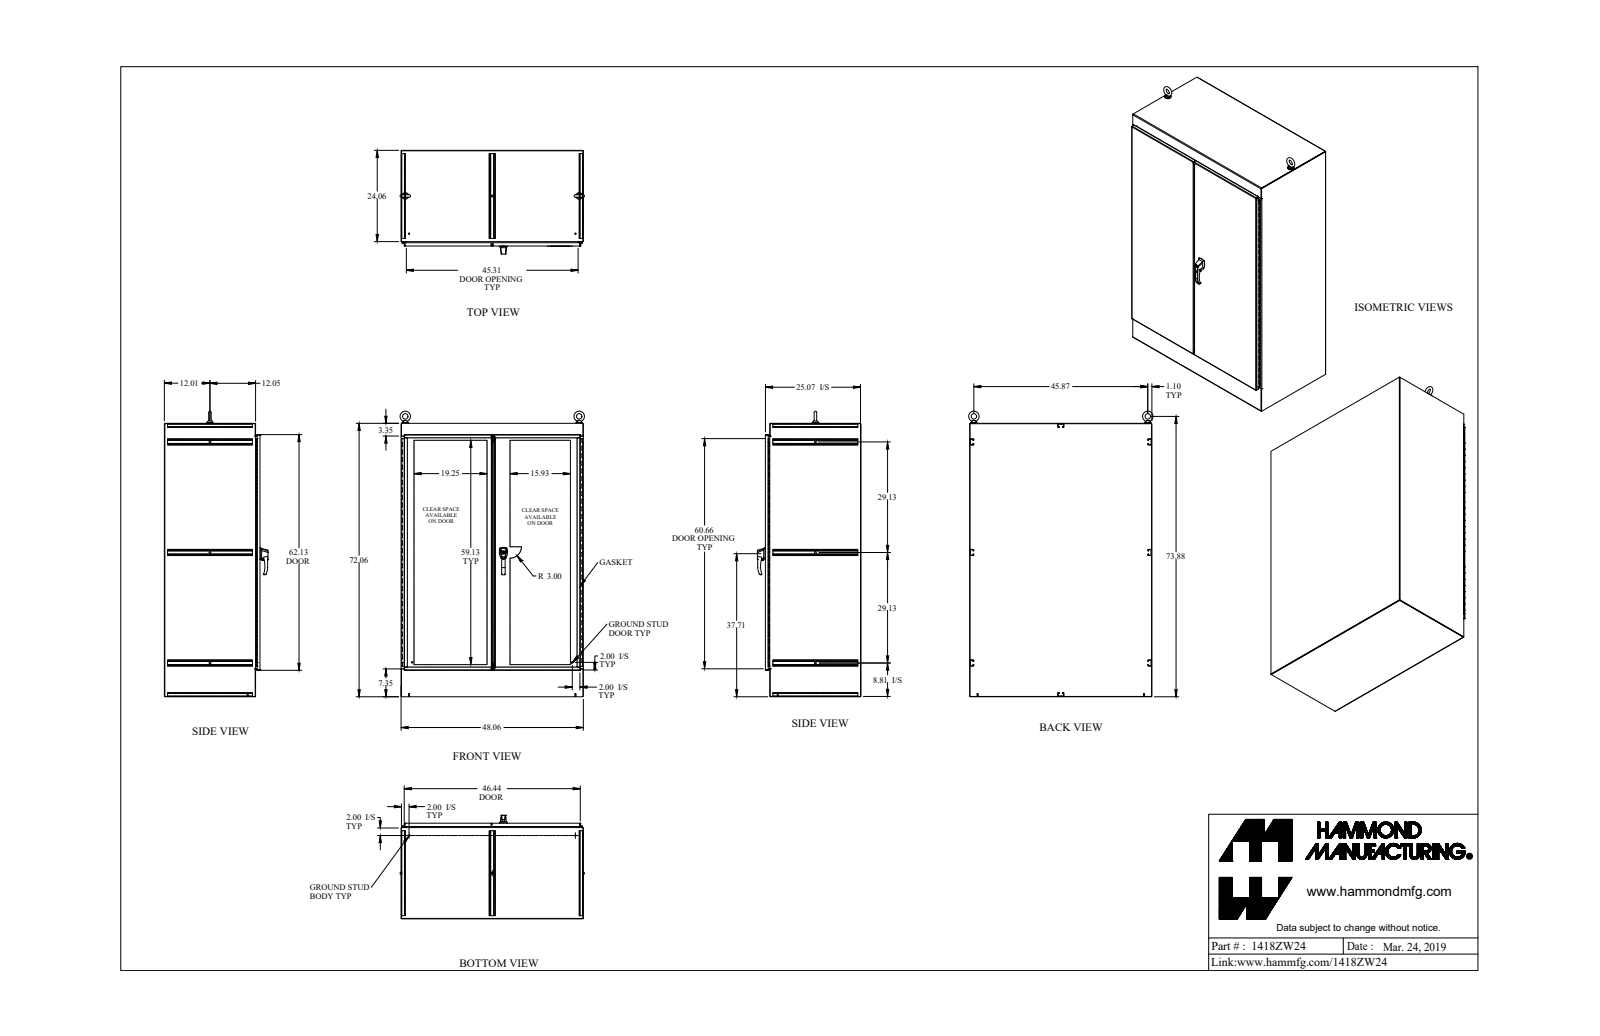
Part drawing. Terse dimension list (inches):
name: 1418ZW24_Default
written by: SolidWorks 2019 (CONFIG_CONTROL_DESIGN)
unit: in
bodies: 71 solids, 2583 faces (1198 planar, 1220 cylindrical, 165 other)
size: 75.713 × 49.119 × 27.337
volume: 1 576 in³; area: 30 814 in²
holes: 20× ⌀0.304, 4× ⌀0.5, 2× ⌀0.11, 2× ⌀0.25, 2× ⌀0.257, 2× ⌀0.28, 2× ⌀0.281, 2× ⌀0.313, 2× ⌀0.39, 2× ⌀0.413, 2× ⌀0.527, 2× ⌀0.625
bosses: 6× ⌀0.281, 4× ⌀0.25, 2× ⌀1.75, 2× ⌀1.5, 2× ⌀1.25, 2× ⌀1, 2× ⌀0.75, 2× ⌀0.738
rounds: 54× R0.043, 48× R0.138, 22× R0.125, 20× R0.048, 20× R0.143, 16× R0.018, 10× R0.06, 8× R0.05
face distances: 0.095, 0.125, 47.965, 25.002, 25.127, 25.097, 25.222, 71.965, 47.87, 48.06
hole spacings: 6, 46.715, 12, 47.857, 18, 49.702, 24, 52.176
